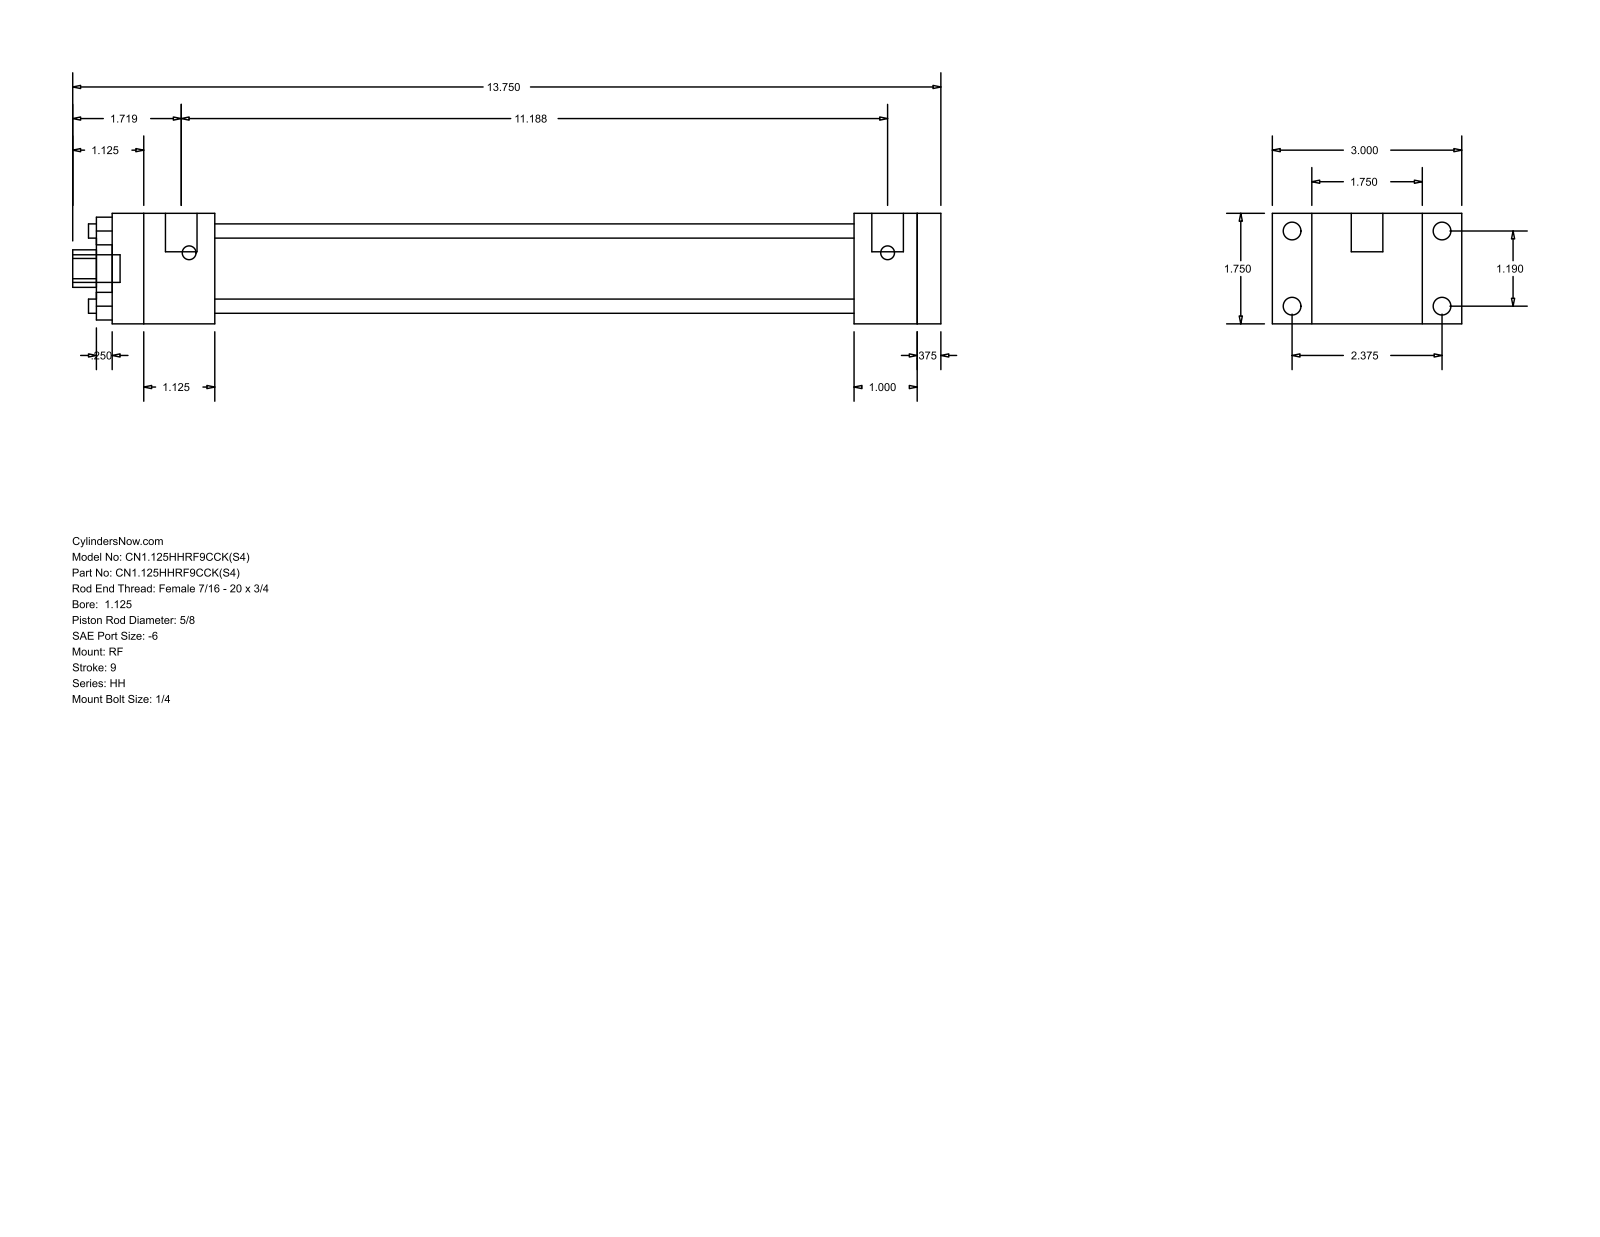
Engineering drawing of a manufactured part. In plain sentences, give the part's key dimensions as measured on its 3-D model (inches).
The part is named "HH_RF__0112_0.625". Its 3-D file was written by "GSSL Pune (CONFIG_CONTROL_DESIGN)". It is 0 solids with 92 faces: 64 planar, 28 cylindrical and 0 other. Overall it measures 13.75 by 3 by 1.75 inches. Round holes: 4 of diameter 0.225, 1 of diameter 0.625, 1 of diameter 1.125, 1 of diameter 1.375. Round bosses or shafts: 4 of diameter 0.281, 4 of diameter 0.219, 2 of diameter 0.5, 1 of diameter 0.437. Partial cylindrical surfaces (rounded edges, fillets, slot ends): 1 of radius 0.297. The main face-to-face distances are 1.75, 0.375, 0.625, 11.125, 11.5, 10.125, 1, 1.375, 1.625, 11.75. The hole center spacings are 0.841, 1.19, 1.683.
